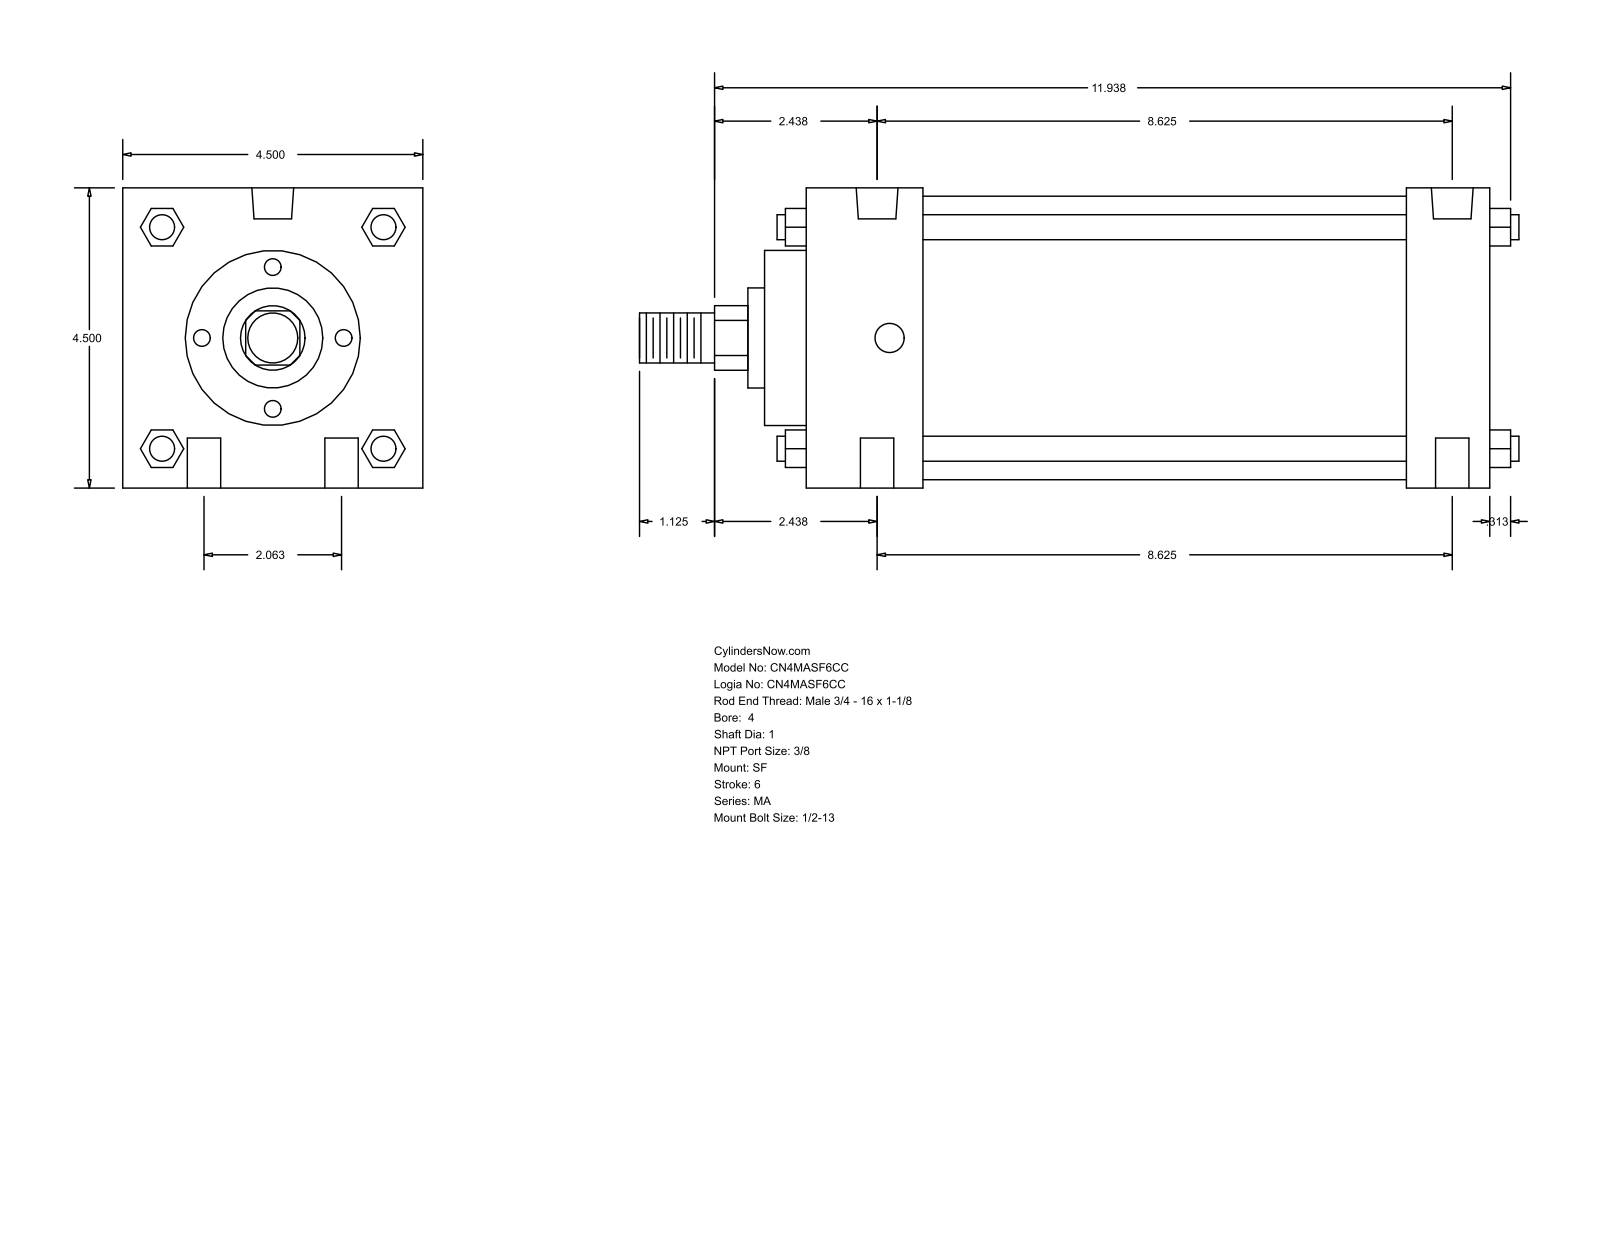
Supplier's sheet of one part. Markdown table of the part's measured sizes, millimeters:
| quantity | value |
| --- | --- |
| part name | MA_SF__0400_1 |
| STEP written by | GSSL Pune (CONFIG_CONTROL_DESIGN) |
| units | millimeters |
| bodies | 0 solids, 126 faces (95 planar, 31 cylindrical, 0 other) |
| overall size | 334.96 × 114.3 × 114.3 |
| round holes (diameter × count) | 12.7 × 4, 11.11 × 2, 15.93 × 2 |
| round bosses / shafts (diameter × count) | 9.53 × 4, 107.95 × 1, 66.67 × 1, 38.1 × 1, 25.4 × 1, 19.05 × 1 |
| partial cylindrical surfaces (radius × count) | 12.29 × 1 |
| main face-to-face distances | 114.3, 260.35, 228.6, 31.75, 44.46, 184.14, 215.89, 276.22, 15.87, 60.33 |
| hole center spacings | 26.19, 220.64, 219.08, 52.38, 225.25, 209.56 |
